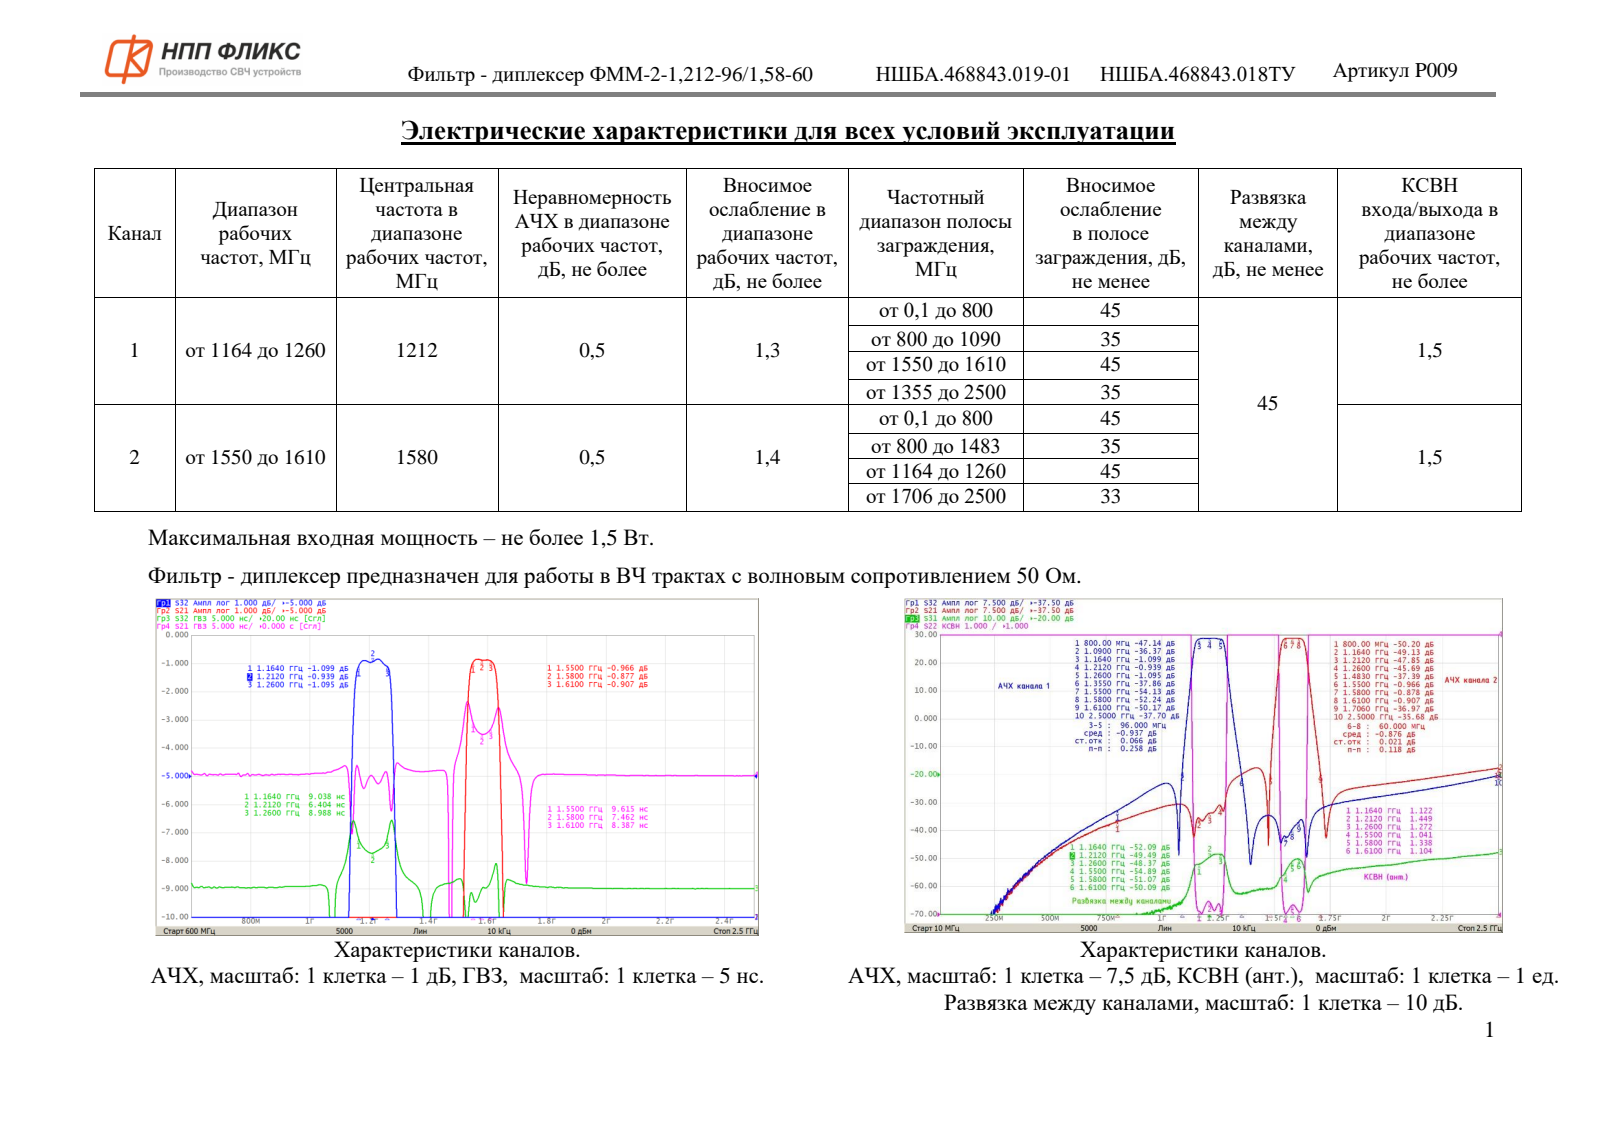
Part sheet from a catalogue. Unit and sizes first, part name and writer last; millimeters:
Units: millimetres
Overall size (bounding box): 18 × 9.75 × 4.2
Partial cylindrical surfaces — rounded edges, fillets, slot ends (radius × count): R0.5 ×23, R0.24 ×3, R0.2 ×2, R0.4 ×2, R0.12 ×1, R0.36 ×1, R0.42 ×1
Main face-to-face distances: 4.2, 1.7, 1.5, 7.85, 9.76, 7.65, 9.56, 6.15, 8.06, 1.91
Volume: 551 mm³ · Surface area: 668 mm²
Bodies: 1 solid, 984 faces (826 planar, 42 cylindrical, 116 other)
Part name (STEP PRODUCT): НШБА.468843.019-01_Диплексер ФММ-2-1,212-96(1,58-60
STEP written by: ASCON Math Kernel (CONFIG_CONTROL_DESIGN)
